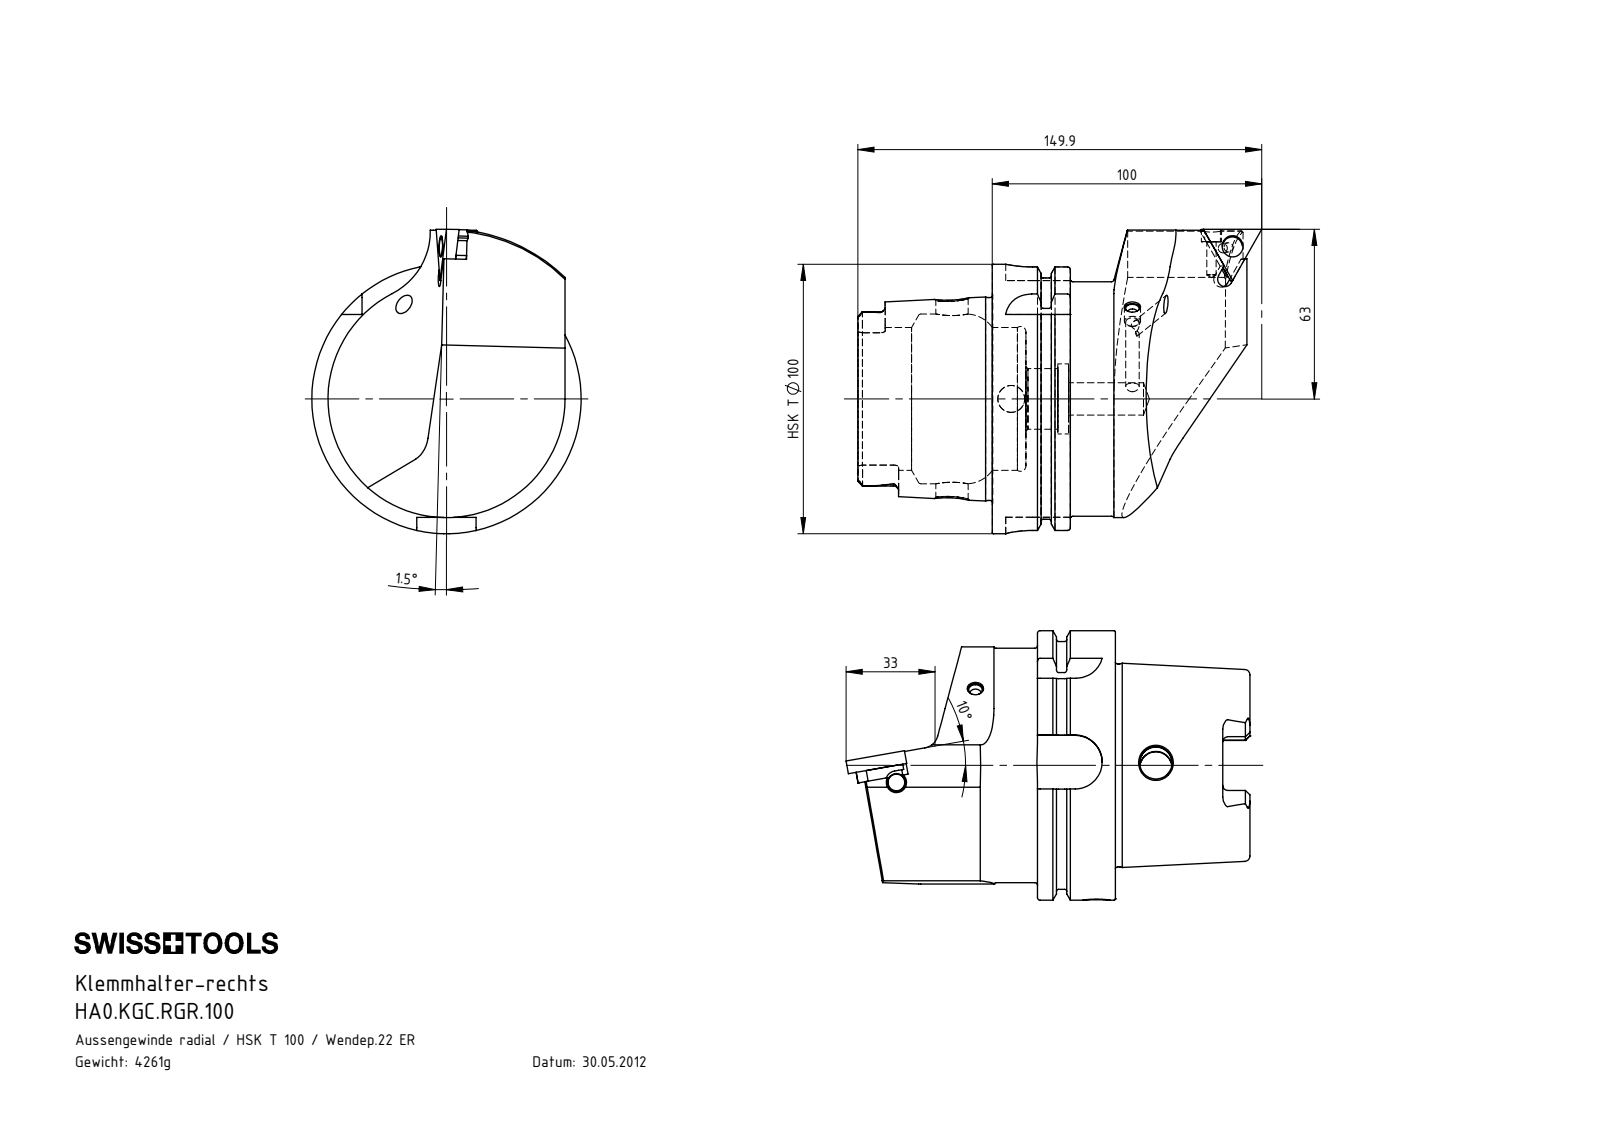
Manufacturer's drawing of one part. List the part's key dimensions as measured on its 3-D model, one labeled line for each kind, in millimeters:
Part name (STEP PRODUCT): HA0-KGC.RGR.100; KVT_MB_600_060; Triag S22 T; LT22NR (+3 more)
STEP written by: SolidWorks 2012 (CONFIG_CONTROL_DESIGN)
Units: millimetres
Bodies: 7 solids, 289 faces (79 planar, 84 cylindrical, 126 other)
Overall size (bounding box): 149.9 × 113 × 100
Volume: 544 042 mm³ · Surface area: 69 649 mm²
Round holes (diameter × count): ⌀3.45 ×2, ⌀5 ×2, ⌀12 ×2, ⌀4.88 ×1, ⌀5.3 ×1, ⌀10 ×1, ⌀22.5 ×1, ⌀26 ×1, ⌀53 ×1, ⌀63 ×1
Round bosses / shafts (diameter × count): ⌀4.1 ×2, ⌀100 ×1, ⌀91.95 ×1, ⌀87 ×1, ⌀75.26 ×1, ⌀6.6 ×1, ⌀6 ×1
Partial cylindrical surfaces — rounded edges, fillets, slot ends (radius × count): R1.9 ×6, R4.88 ×4, R10 ×4, R1.5 ×1, R2 ×1, R2.75 ×1, R3.75 ×1, R4 ×1
Main face-to-face distances: 12.45, 28.95, 16.5, 49.9, 62.35, 78.85, 87.8, 78.2, 28.3, 15.85
